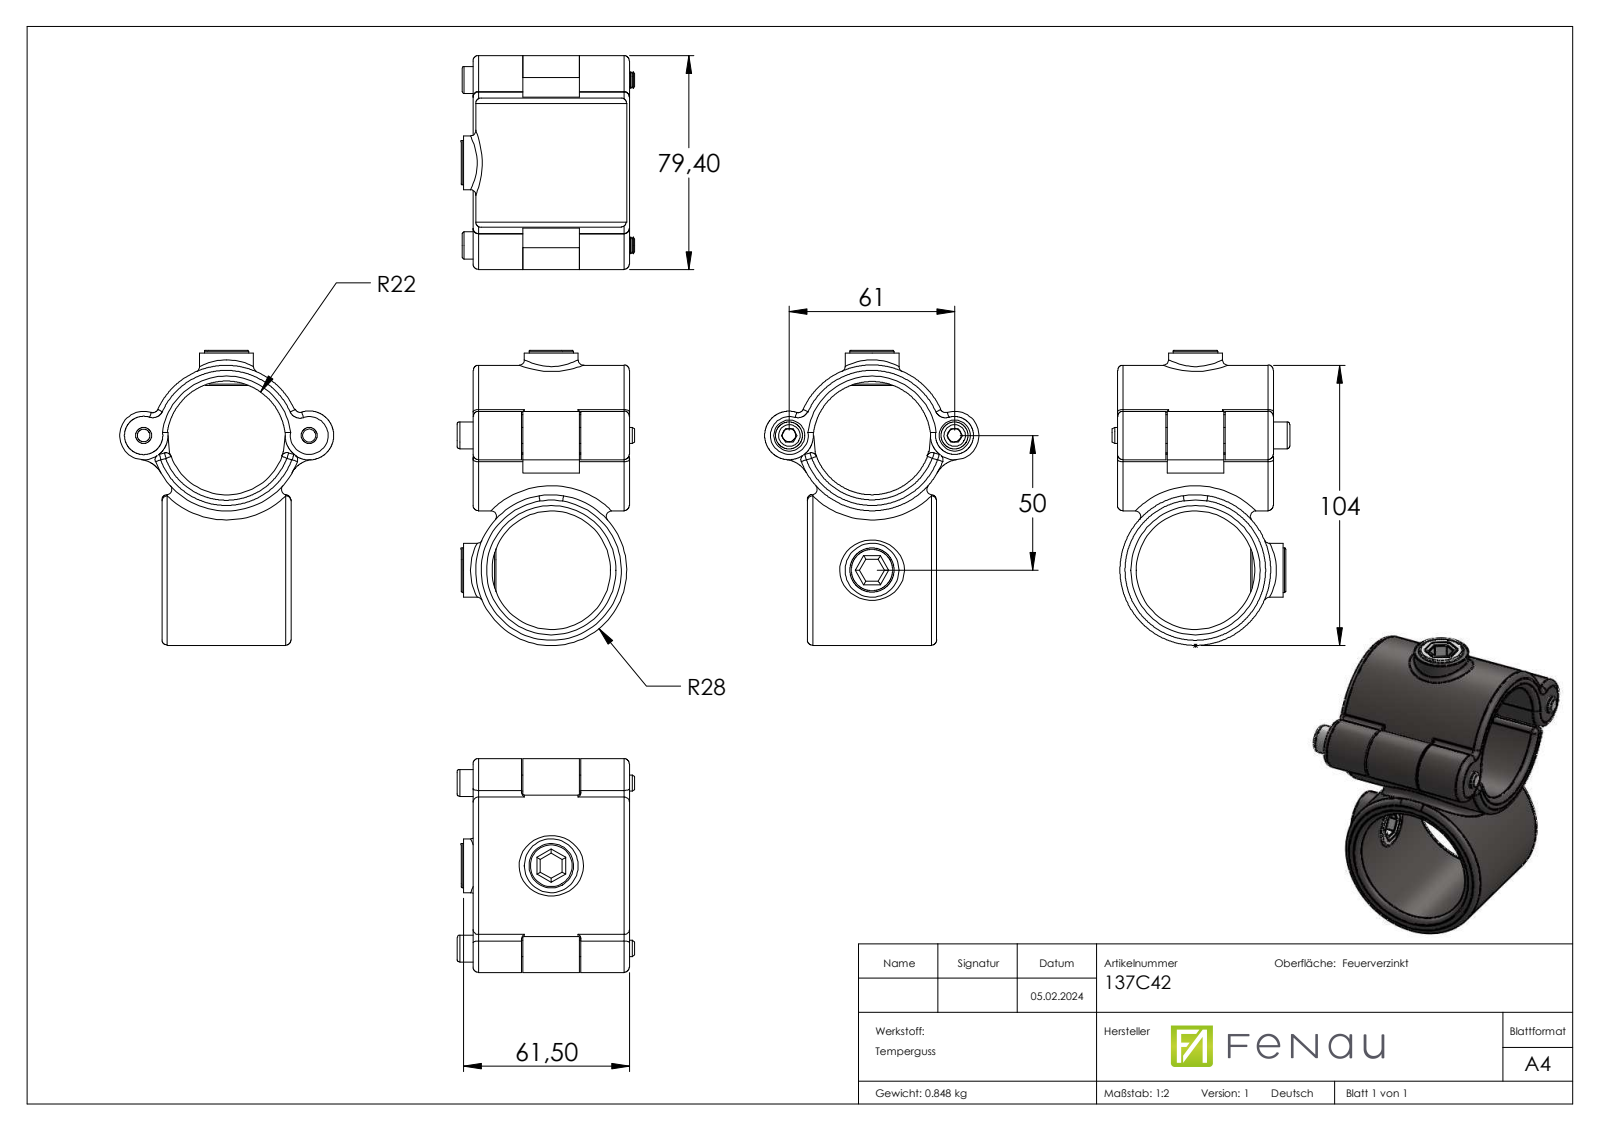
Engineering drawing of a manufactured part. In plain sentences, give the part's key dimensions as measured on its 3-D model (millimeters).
The part is named "137-C42 Teil1_137-C42 Teil1; 137-C42 Teil3_137-C42 Teil3; 137-C42; 137-C42 Teil2_137-C42 Teil2 (+1 more)". Its 3-D file was written by "SolidWorks 2018 (CONFIG_CONTROL_DESIGN)". It is 6 solids with 196 faces: 70 planar, 75 cylindrical and 51 other. Overall it measures 109.59 by 79.4 by 66 millimeters. Its volume is 115 511 cubic millimeters and its surface area 47 155 square millimeters. Round holes: 2 of diameter 5, 2 of diameter 7.5, 2 of diameter 15.25, 1 of diameter 25, 1 of diameter 44. Round bosses or shafts: 2 of diameter 20, 2 of diameter 18, 2 of diameter 16.5, 2 of diameter 10, 2 of diameter 6, 1 of diameter 56. Partial cylindrical surfaces (rounded edges, fillets, slot ends): 34 of radius 2, 4 of radius 1, 2 of radius 10, 2 of radius 22, 2 of radius 28. The main face-to-face distances are 21.5, 18.5, 39.5, 0.5, 18, 40, 22, 58, 21, 8.1. The hole center spacings are 58.67, 61.4.
